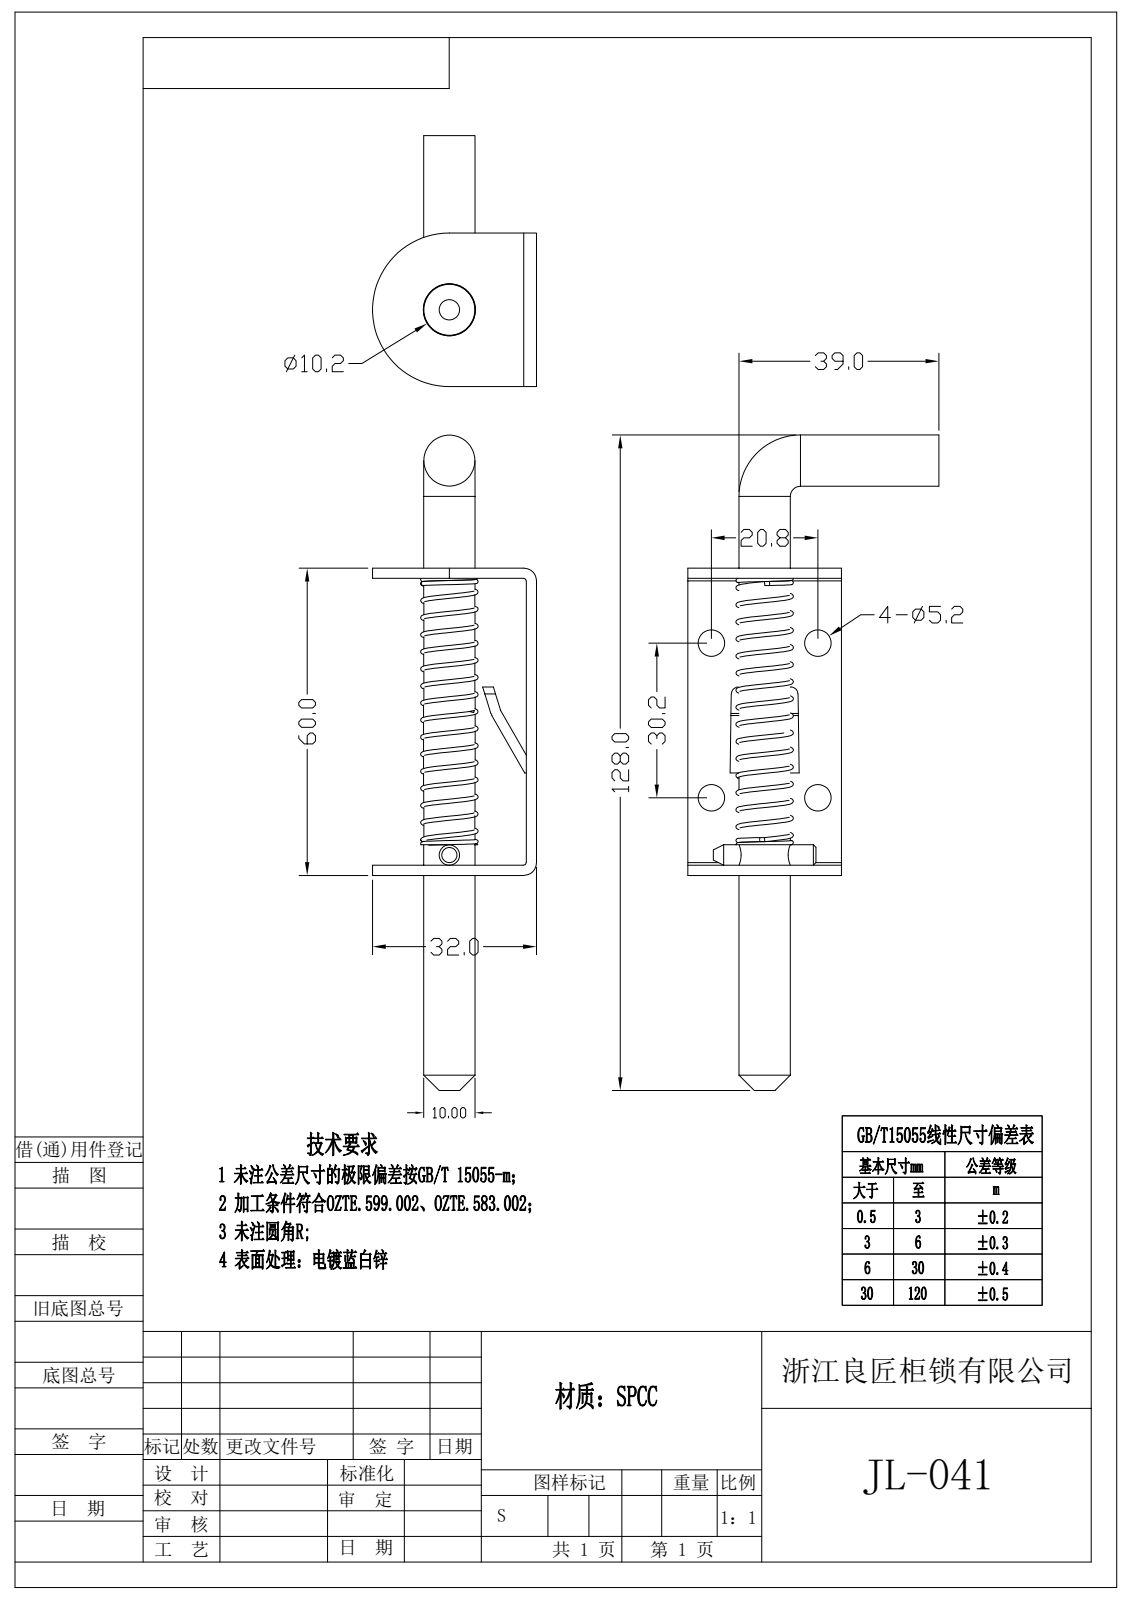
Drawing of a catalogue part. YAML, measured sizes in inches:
step_written_by: "Rhino 8.5 (CONFIG_CONTROL_DESIGN)"
units: inches
bodies: {solids: 3, faces: 86, planar: 40, cylindrical: 36, other: 10}
overall_size: [5.039, 1.929, 1.181]
volume: 0.769
surface_area: 22.83
round_holes:
  - {diameter: 0.157, count: 1}
  - {diameter: 0.173, count: 1}
round_bosses_or_shafts:
  - {diameter: 0.394, count: 2}
  - {diameter: 0.402, count: 1}
partial_cylinders:
  - {radius: 0.054, count: 4}
  - {radius: 0.02, count: 2}
  - {radius: 0.098, count: 2}
  - {radius: 0.079, count: 1}
  - {radius: 0.591, count: 1}
face_to_face_distances: [0.079, 2.283, 2.205, 2.362, 1.181, 0.669, 0.748, 0.709, 0.081, 0.787]
